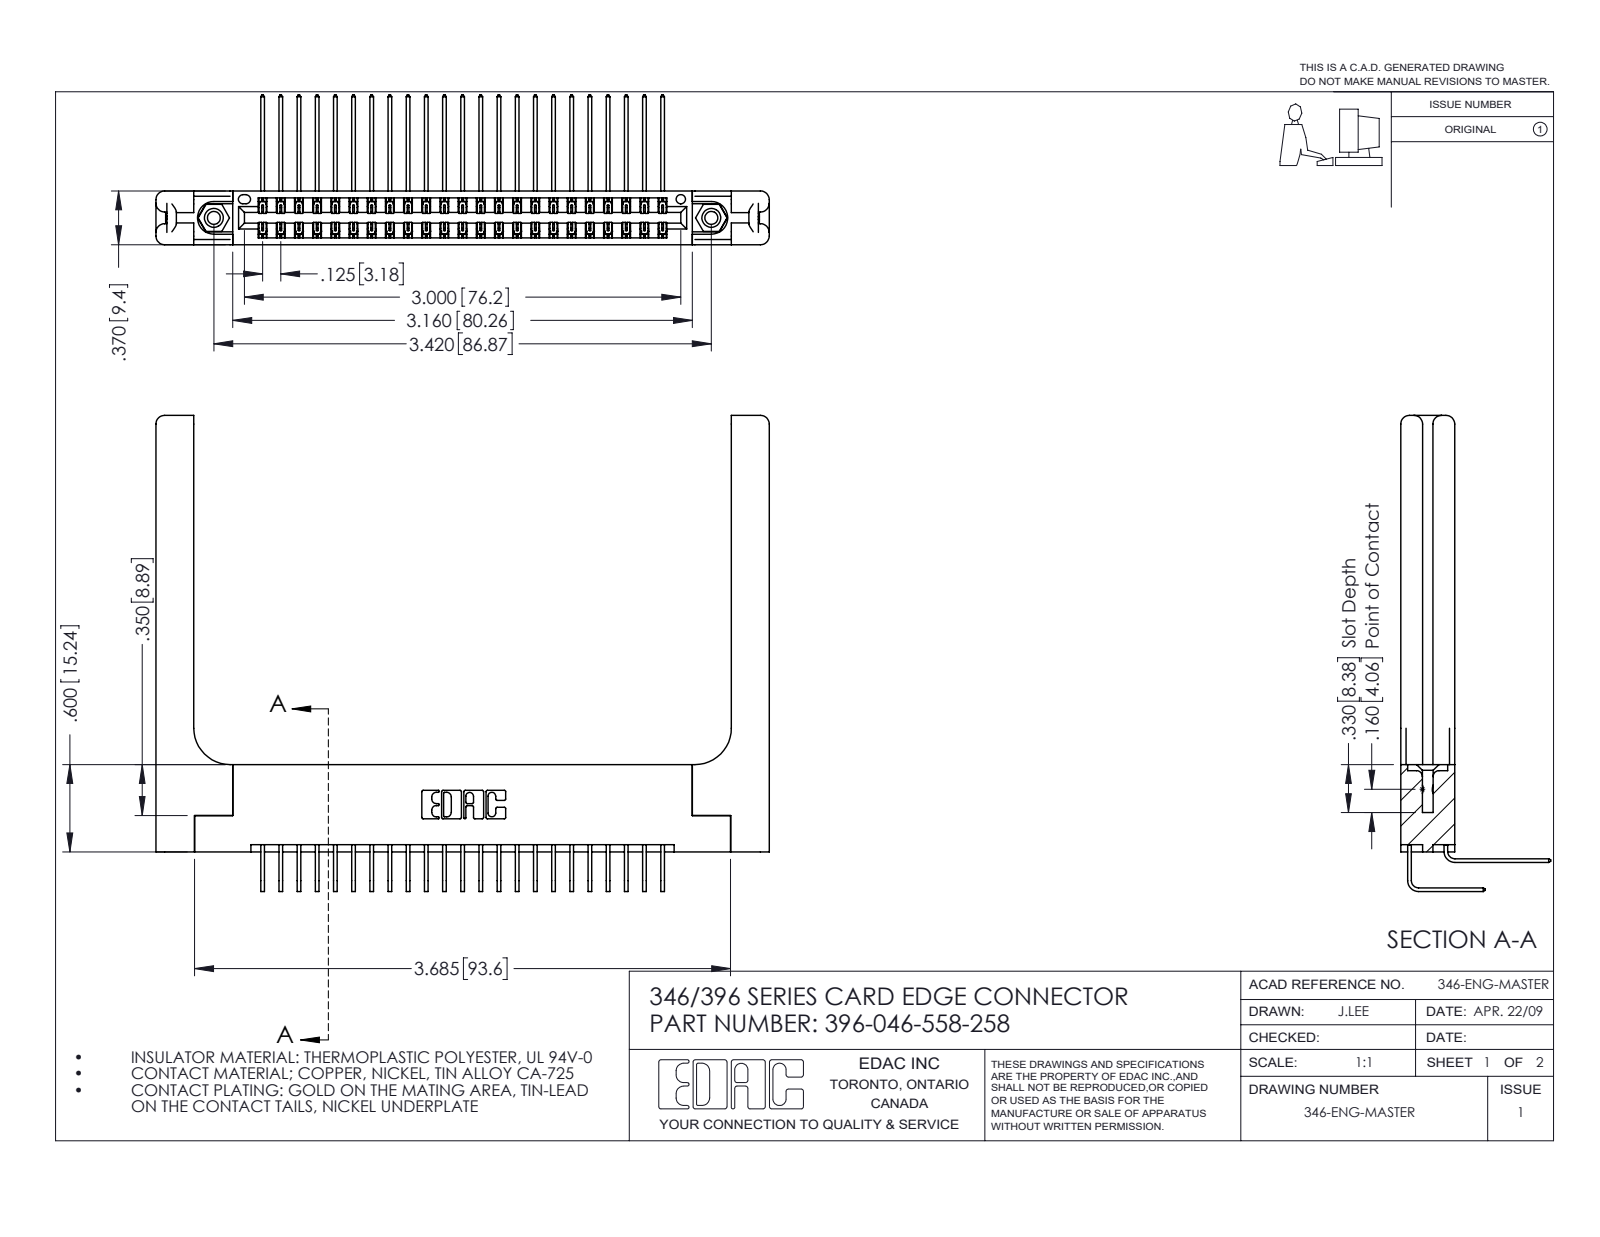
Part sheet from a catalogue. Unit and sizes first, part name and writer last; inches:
Units: inches
Overall size (bounding box): 4.216 × 3.273 × 1.03
Round holes (diameter × count): ⌀0.089 ×2, ⌀0.125 ×2, ⌀0.156 ×2, ⌀0.064 ×1
Round bosses / shafts (diameter × count): ⌀0.155 ×2
Partial cylindrical surfaces — rounded edges, fillets, slot ends (radius × count): R0.006 ×69, R0.01 ×22, R0.06 ×16, R0.007 ×6, R0.031 ×6, R0.026 ×3, R0.014 ×2, R0.022 ×2
Main face-to-face distances: 0.37, 0.322, 0.072, 0.048, 0.148, 0.15, 0.025, 0.298, 0.25, 0.077
Hole centre spacings: 0.246, 3.212, 3.42
Volume: 1.102 in³ · Surface area: 31.72 in²
Bodies: 51 solids, 2862 faces (1926 planar, 876 cylindrical, 60 other)
Part name (STEP PRODUCT): 345-292-001_558 Tail - 2; 345-292-001_558 559 Tail - 1; 396-046-558-258; 346 Part_Flush Mounting Lugs - 0.156 Dia-TH (+2 more)
STEP written by: SolidWorks 2016 (CONFIG_CONTROL_DESIGN)
